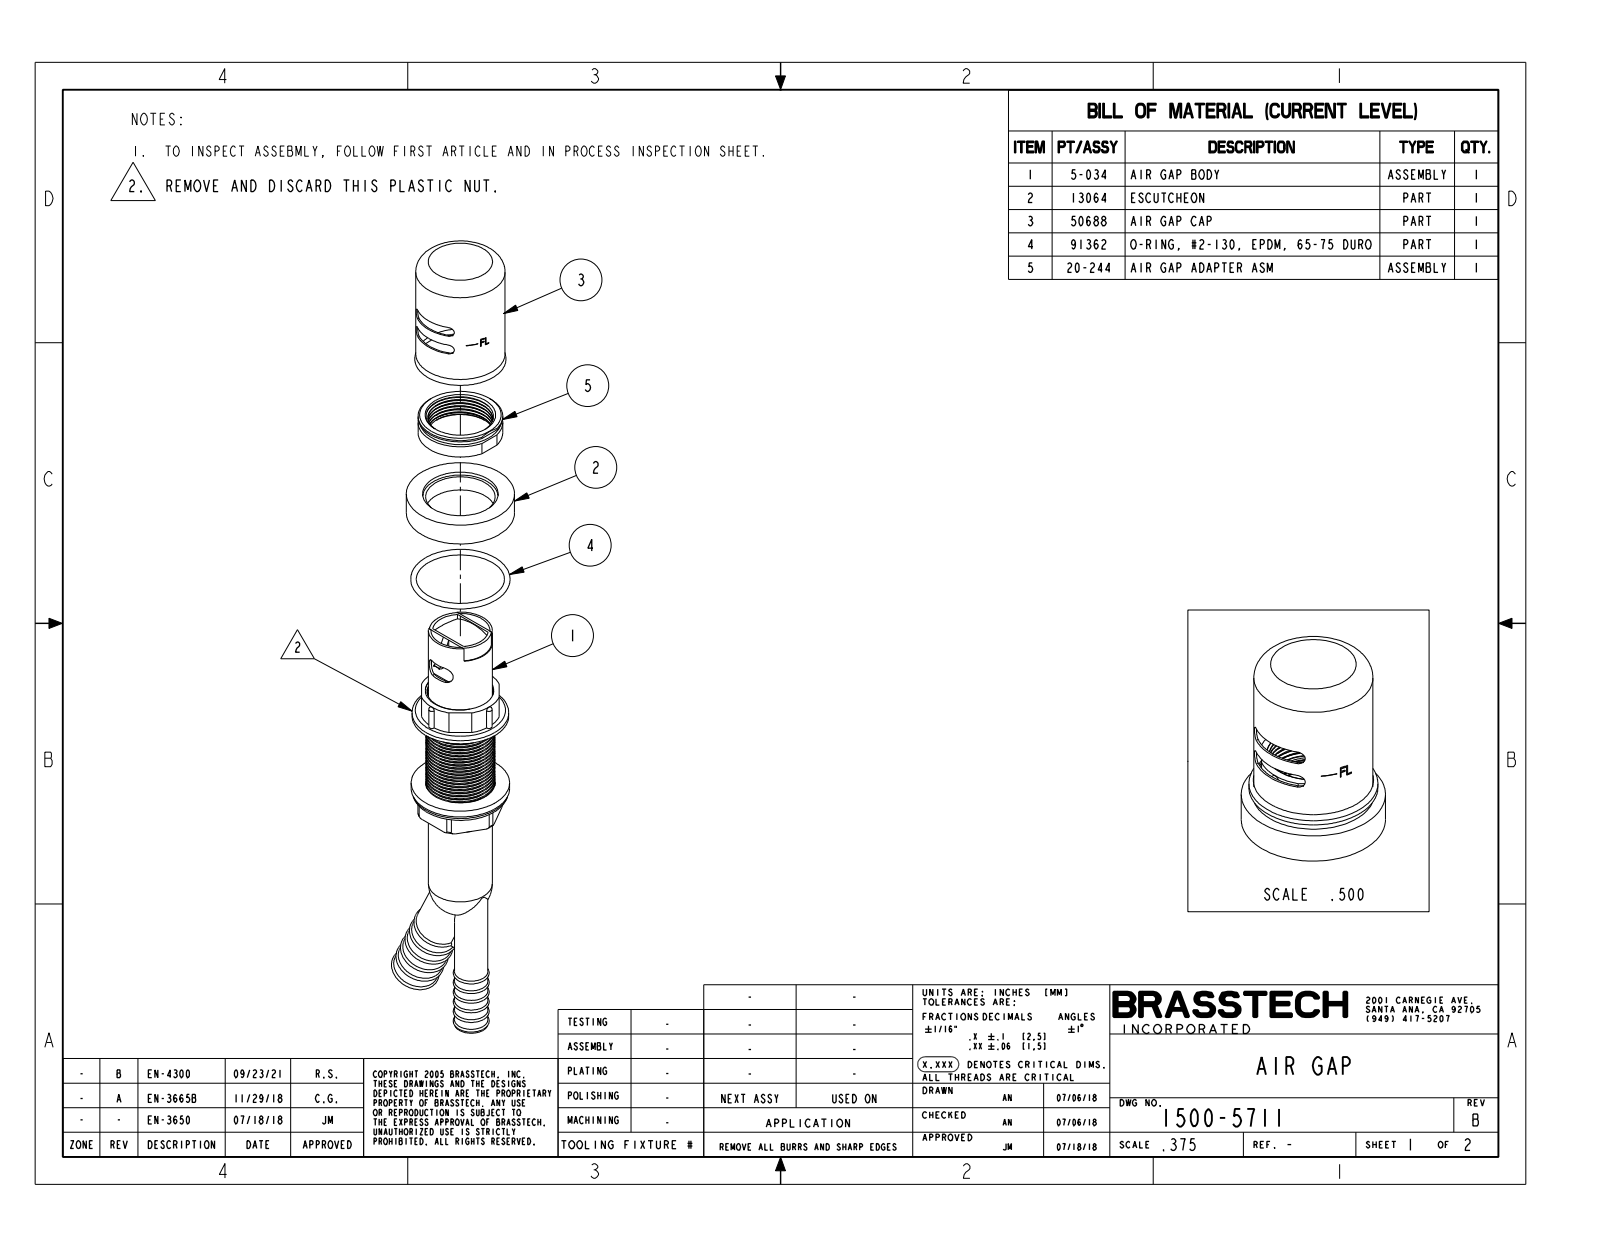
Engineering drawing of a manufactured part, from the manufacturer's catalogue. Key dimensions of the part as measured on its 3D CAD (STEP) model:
Part name (STEP PRODUCT): 1500-5711
STEP written by: CREO PARAMETRIC BY PTC INC, 2018400 (AUTOMOTIVE_DESIGN)
Units: inches
Bodies: 1 solid, 267 faces (68 planar, 130 cylindrical, 69 other)
Overall size (bounding box): 8.846 × 2.572 × 1.98
Volume: 10.2 in³ · Surface area: 79.43 in²
Round holes (diameter × count): ⌀1.2 ×1, ⌀1.27 ×1, ⌀1.28 ×1, ⌀1.575 ×1
Round bosses / shafts (diameter × count): ⌀1.98 ×1, ⌀1.8 ×1, ⌀1.76 ×1, ⌀1.669 ×1, ⌀1.635 ×1, ⌀1.259 ×1, ⌀1.17 ×1, ⌀0.854 ×1
Partial cylindrical surfaces — rounded edges, fillets, slot ends (radius × count): R0.04 ×6, R0.098 ×4, R0.157 ×2, R0.808 ×1
Main face-to-face distances: 0.964, 3.549, 3.579, 2.585, 2.615, 0.03, 1.389, 0.425, 2.16, 2.19
